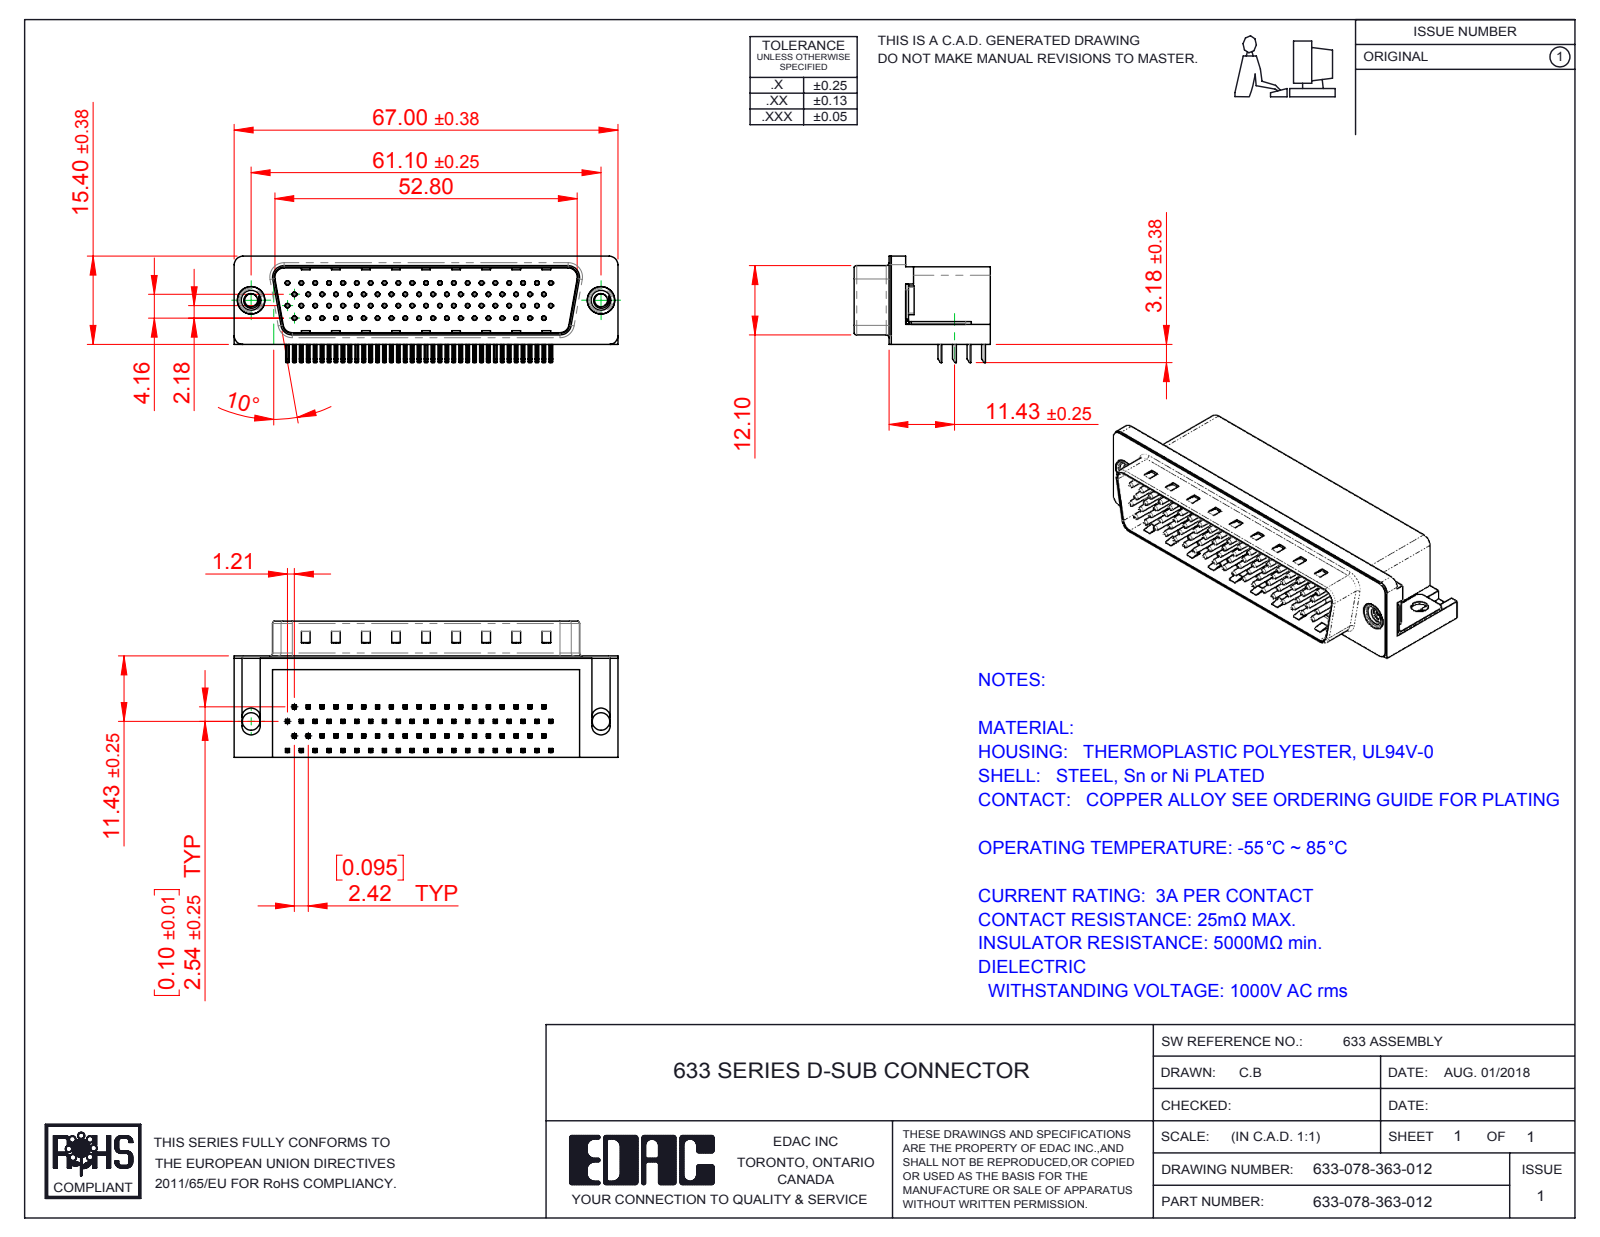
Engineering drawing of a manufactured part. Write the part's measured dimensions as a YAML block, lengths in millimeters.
part_name: "633 Contact Top_78 Contact; 633-078-363-012; 633 Shell_78 Contact; 633 Contact Bottom_78 Contact (+5 more)"
step_written_by: "SolidWorks 2016 (CONFIG_CONTROL_DESIGN)"
units: millimeters
bodies: {solids: 84, faces: 6274, planar: 3979, cylindrical: 1778, other: 517}
overall_size: [67, 23.8, 18.58]
volume: 14612
surface_area: 16336
round_holes:
  - {diameter: 0.35, count: 78}
  - {diameter: 0.8, count: 78}
  - {diameter: 2.26, count: 2}
  - {diameter: 3.05, count: 2}
  - {diameter: 4, count: 2}
  - {diameter: 4.8, count: 2}
  - {diameter: 5, count: 2}
round_bosses_or_shafts:
  - {diameter: 0.75, count: 78}
  - {diameter: 4.9, count: 2}
  - {diameter: 4.75, count: 2}
  - {diameter: 3.9, count: 2}
partial_cylinders:
  - {radius: 0.25, count: 320}
  - {radius: 0.12, count: 156}
  - {radius: 1, count: 16}
  - {radius: 0.5, count: 9}
  - {radius: 1.6, count: 8}
  - {radius: 1.5, count: 6}
  - {radius: 0.45, count: 4}
  - {radius: 0.9, count: 4}
face_to_face_distances: [0.4, 13.2, 17.3, 11.7, 13.35, 2.05, 13.75, 1.65, 1.85, 11.9]
hole_center_spacings: [2.42, 4.84, 7.26, 9.68, 6.26, 7.13, 12.1, 8.62]
